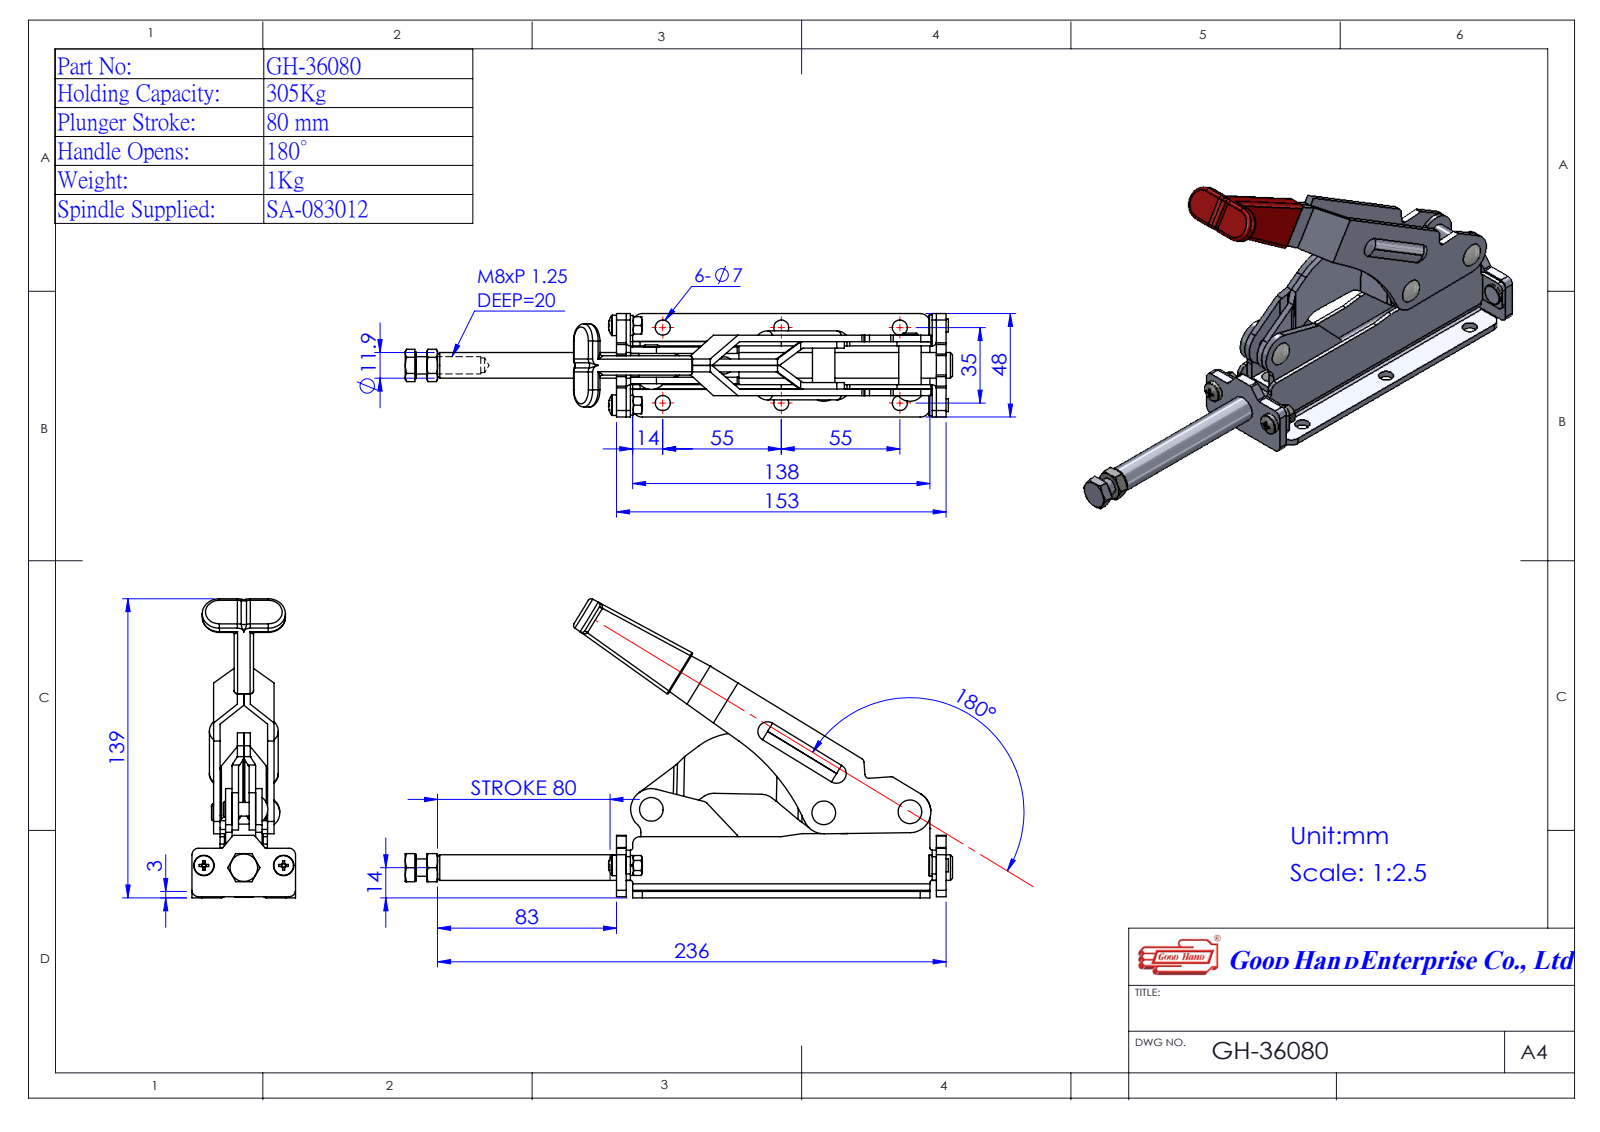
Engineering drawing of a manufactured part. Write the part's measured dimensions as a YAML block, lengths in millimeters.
part_name: "Group3^組合件36-GH-36080; Group2^組合件36-GH-36080; Group1^組合件36-GH-36080; GH-36080 (+2 more)"
step_written_by: "SolidWorks 2016 (AUTOMOTIVE_DESIGN)"
units: millimeters
bodies: {solids: 6, faces: 388, planar: 161, cylindrical: 157, other: 70}
overall_size: [255.24, 138.72, 48]
volume: 137893
surface_area: 84097
round_holes:
  - {diameter: 7, count: 6}
  - {diameter: 6.33, count: 2}
  - {diameter: 6.4, count: 2}
  - {diameter: 11.9, count: 2}
  - {diameter: 6.8, count: 1}
  - {diameter: 8, count: 1}
round_bosses_or_shafts:
  - {diameter: 7.3, count: 3}
  - {diameter: 6.3, count: 2}
  - {diameter: 12.5, count: 1}
partial_cylinders:
  - {radius: 3, count: 15}
  - {radius: 1, count: 8}
  - {radius: 1.6, count: 6}
  - {radius: 4.5, count: 6}
  - {radius: 2, count: 5}
  - {radius: 0.5, count: 4}
  - {radius: 1.5, count: 4}
  - {radius: 8, count: 2}
face_to_face_distances: [3, 5.5, 2.5, 2, 22, 20, 25, 8.5, 19.5, 14]
hole_center_spacings: [55, 65.19, 35, 110, 115.43, 40, 80.04, 120.03]
